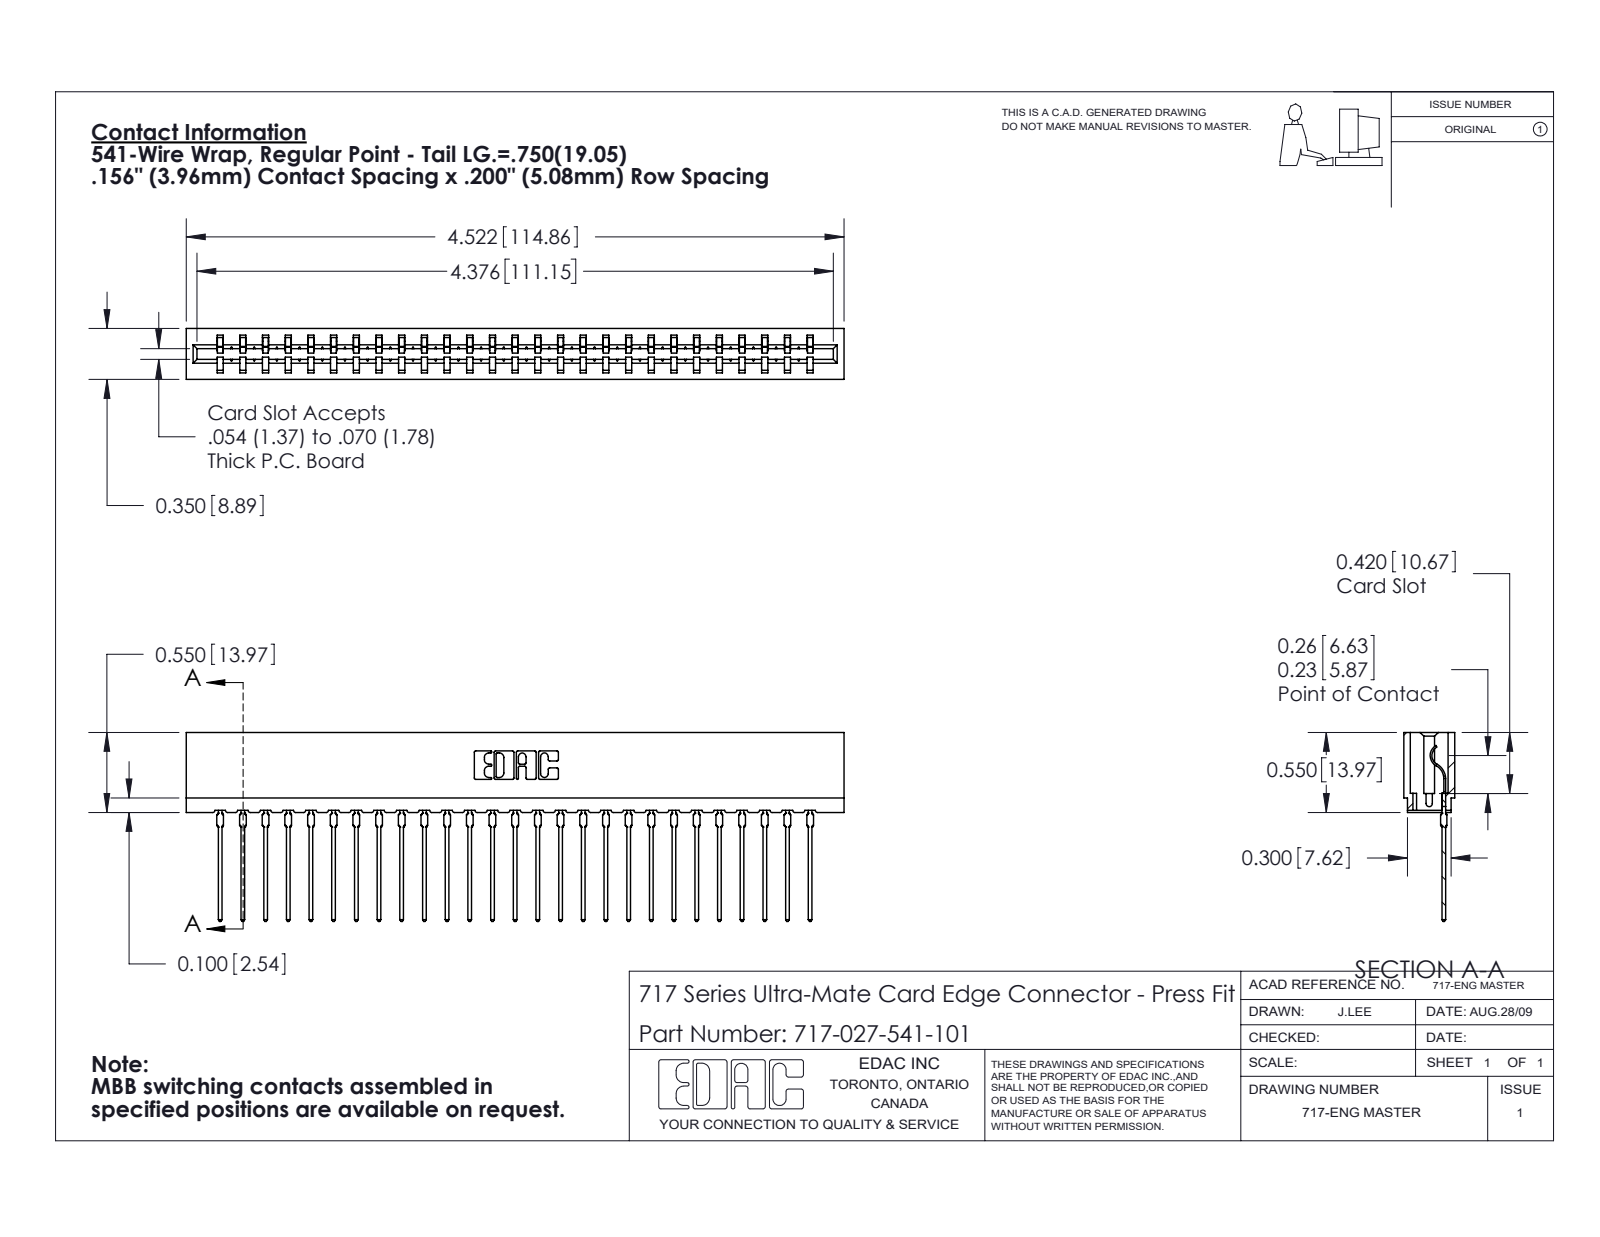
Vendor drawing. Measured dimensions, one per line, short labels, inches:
name: 717 Part_Insulator Option - 06; 717-027-541-101; 745-292-001_541
written by: SolidWorks 2020 (CONFIG_CONTROL_DESIGN)
unit: in
bodies: 28 solids, 3145 faces (1890 planar, 553 cylindrical, 702 other)
size: 4.522 × 1.299 × 0.35
volume: 0.603 in³; area: 22.14 in²
rounds: 54× R0.015, 54× R0.021, 22× R0.01, 6× R0.007, 6× R0.031, 4× R0.005, 4× R0.011, 3× R0.026
face distances: 0.212, 0.138, 0.35, 0.156, 0.063, 0.287, 0.076, 0.149, 0.074, 0.045
